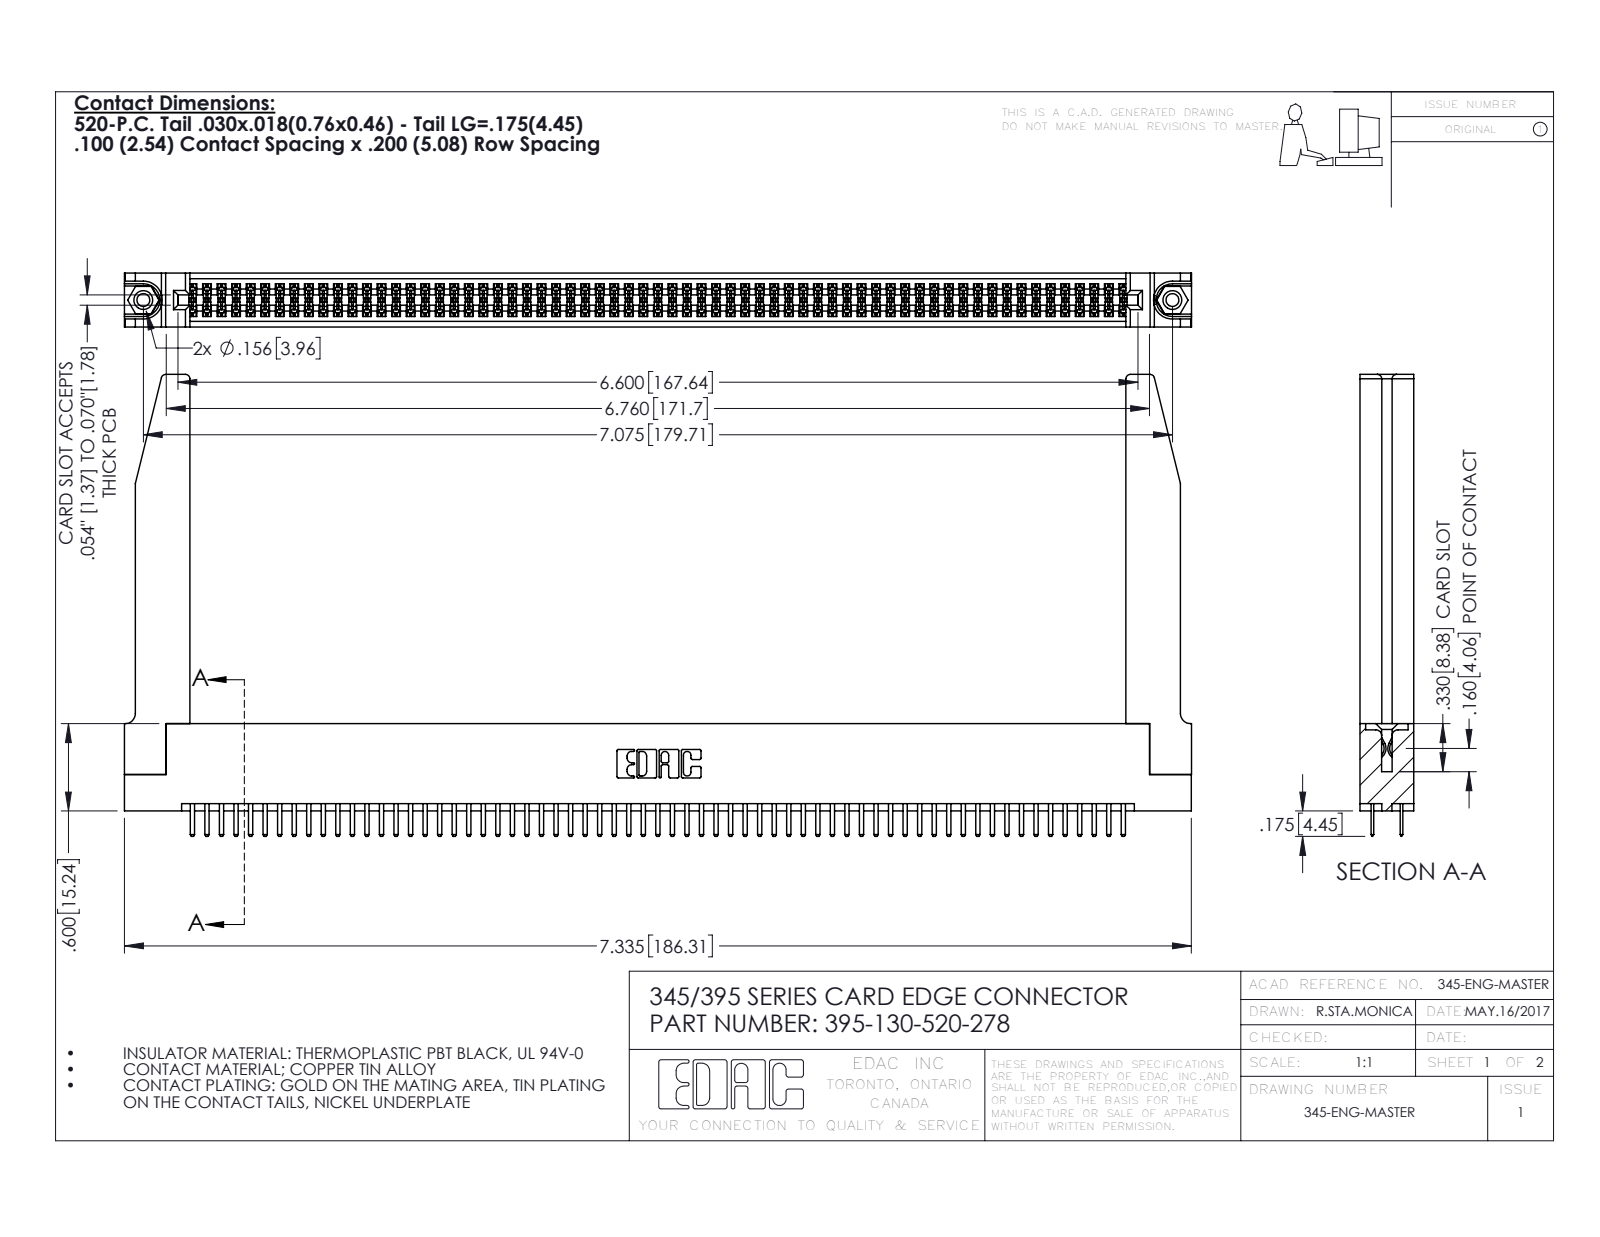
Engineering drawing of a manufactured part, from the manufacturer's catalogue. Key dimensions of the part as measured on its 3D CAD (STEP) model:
Part name (STEP PRODUCT): 345-250-001_345-250-001-102; 345-292-001_345-293-120; 395-130-520-278; 345 Part_Flush Mounting Lugs - 0.156 Dia-TH (+1 more)
STEP written by: SolidWorks 2016 (CONFIG_CONTROL_DESIGN)
Units: inches
Bodies: 135 solids, 7380 faces (4772 planar, 2556 cylindrical, 52 other)
Overall size (bounding box): 7.336 × 3.175 × 0.37
Volume: 1.588 in³ · Surface area: 52.93 in²
Round holes (diameter × count): ⌀0.089 ×2, ⌀0.125 ×2, ⌀0.156 ×2, ⌀0.064 ×1
Round bosses / shafts (diameter × count): ⌀0.155 ×2
Partial cylindrical surfaces — rounded edges, fillets, slot ends (radius × count): R0.006 ×195, R0.01 ×134, R0.01 ×22, R0.03 ×8, R0.007 ×6, R0.031 ×6, R0.026 ×3, R0.014 ×2
Main face-to-face distances: 0.072, 0.37, 0.298, 0.2, 0.098, 0.272, 0.025, 0.225, 0.022, 0.072
Hole centre spacings: 0.27, 6.839, 7.075
